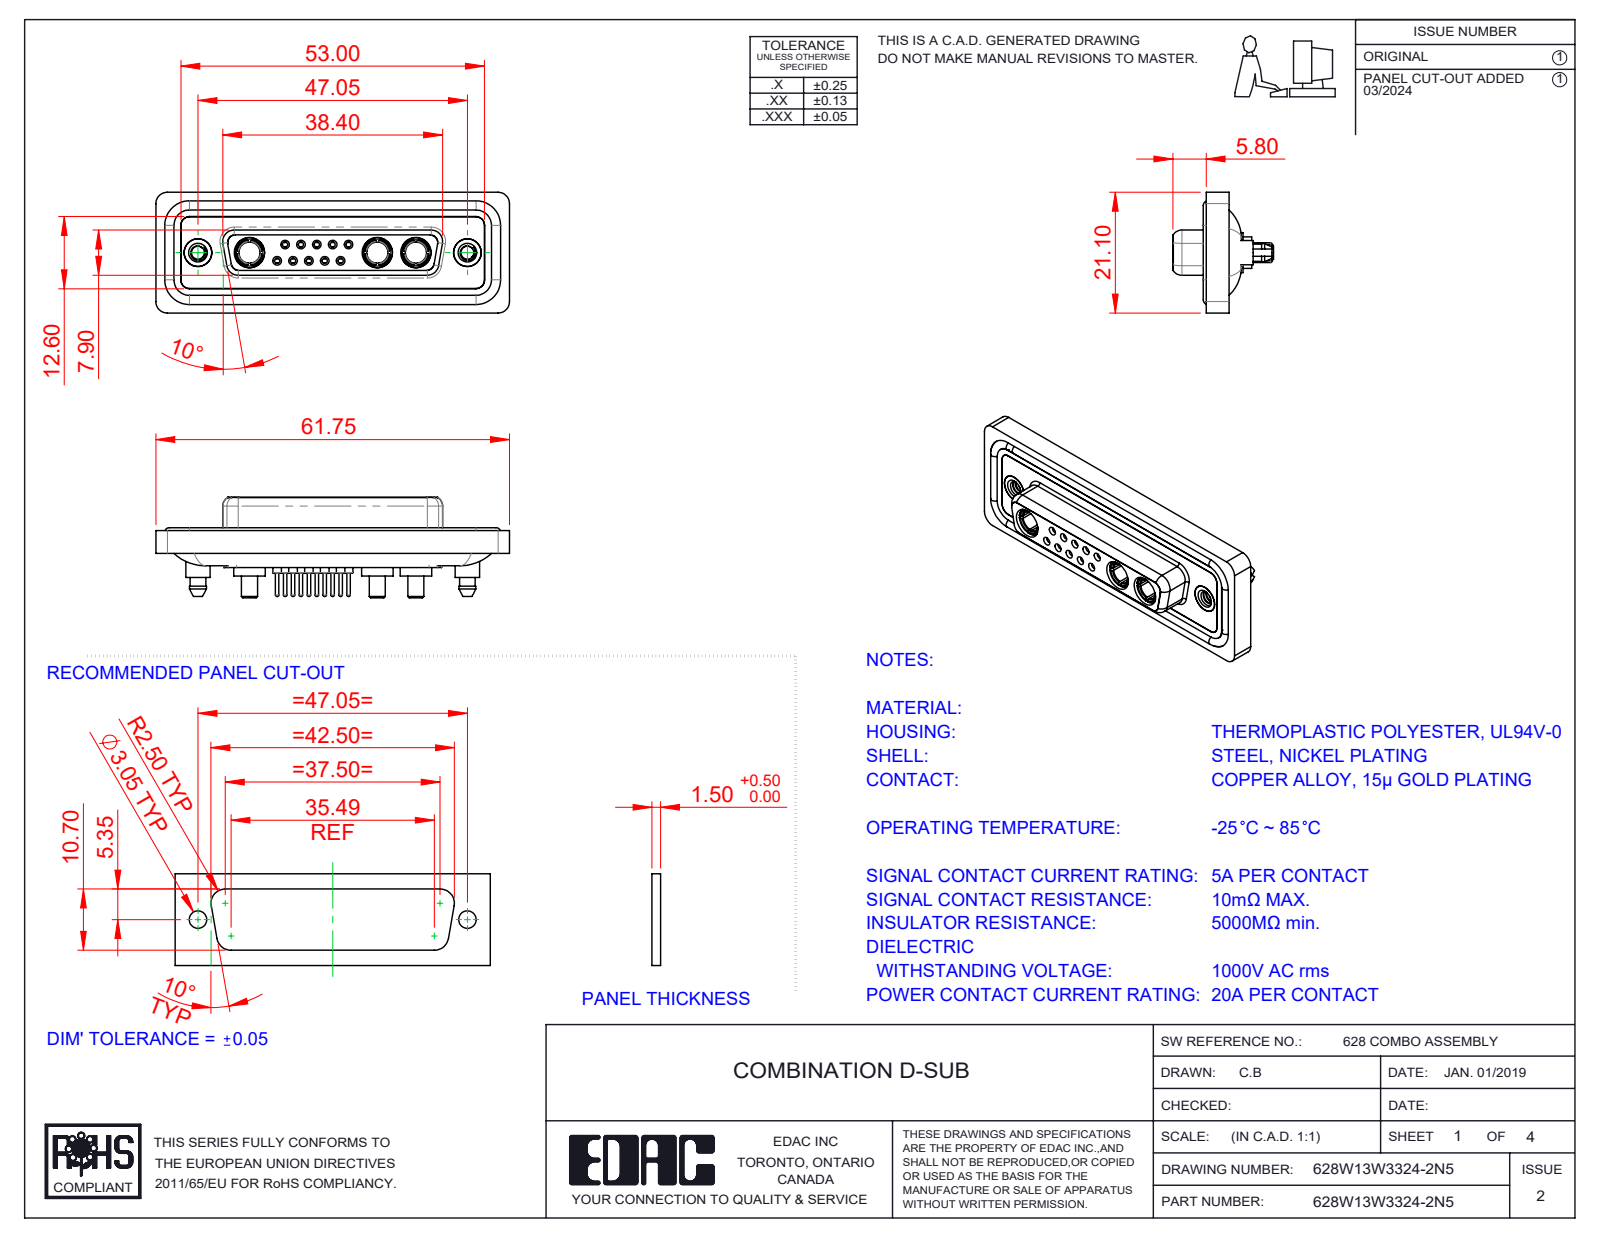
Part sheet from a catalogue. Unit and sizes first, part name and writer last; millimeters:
Units: millimetres
Overall size (bounding box): 61.75 × 21.1 × 17.55
Round holes (diameter × count): ⌀0.9 ×10, ⌀1.1 ×10, ⌀1.5 ×10, ⌀2 ×10, ⌀1.6 ×5, ⌀1.7 ×5, ⌀4.85 ×5, ⌀3.7 ×3, ⌀5.3 ×3, ⌀2.26 ×2, ⌀4 ×2, ⌀4.05 ×2
Round bosses / shafts (diameter × count): ⌀2.2 ×10, ⌀0.6 ×10, ⌀1.6 ×9, ⌀5.5 ×3, ⌀5.2 ×3, ⌀4.96 ×3, ⌀4.75 ×3, ⌀3.75 ×3
Partial cylindrical surfaces — rounded edges, fillets, slot ends (radius × count): R1.5 ×24, R2 ×18, R1.6 ×10, R1.35 ×8, R0.25 ×4, R0.5 ×4, R0.6 ×4, R0.65 ×4
Main face-to-face distances: 0.4, 1.8, 7.45, 5.65, 0.5, 6.6, 7.05, 1.6, 2.9, 1.1
Hole centre spacings: 3.16, 2.77, 5.03, 5.04, 5.54, 8.31, 7.49, 2.76
Volume: 8 407 mm³ · Surface area: 14 042 mm²
Bodies: 23 solids, 1208 faces (358 planar, 479 cylindrical, 371 other)
Part name (STEP PRODUCT): 628Combo Shell Rear_25 Contacts; 628W13W3324-2N5; 628Combo Contact Row 2_24; 628Combo Housing_13W3 (+5 more)
STEP written by: SolidWorks 2023 (CONFIG_CONTROL_DESIGN)
